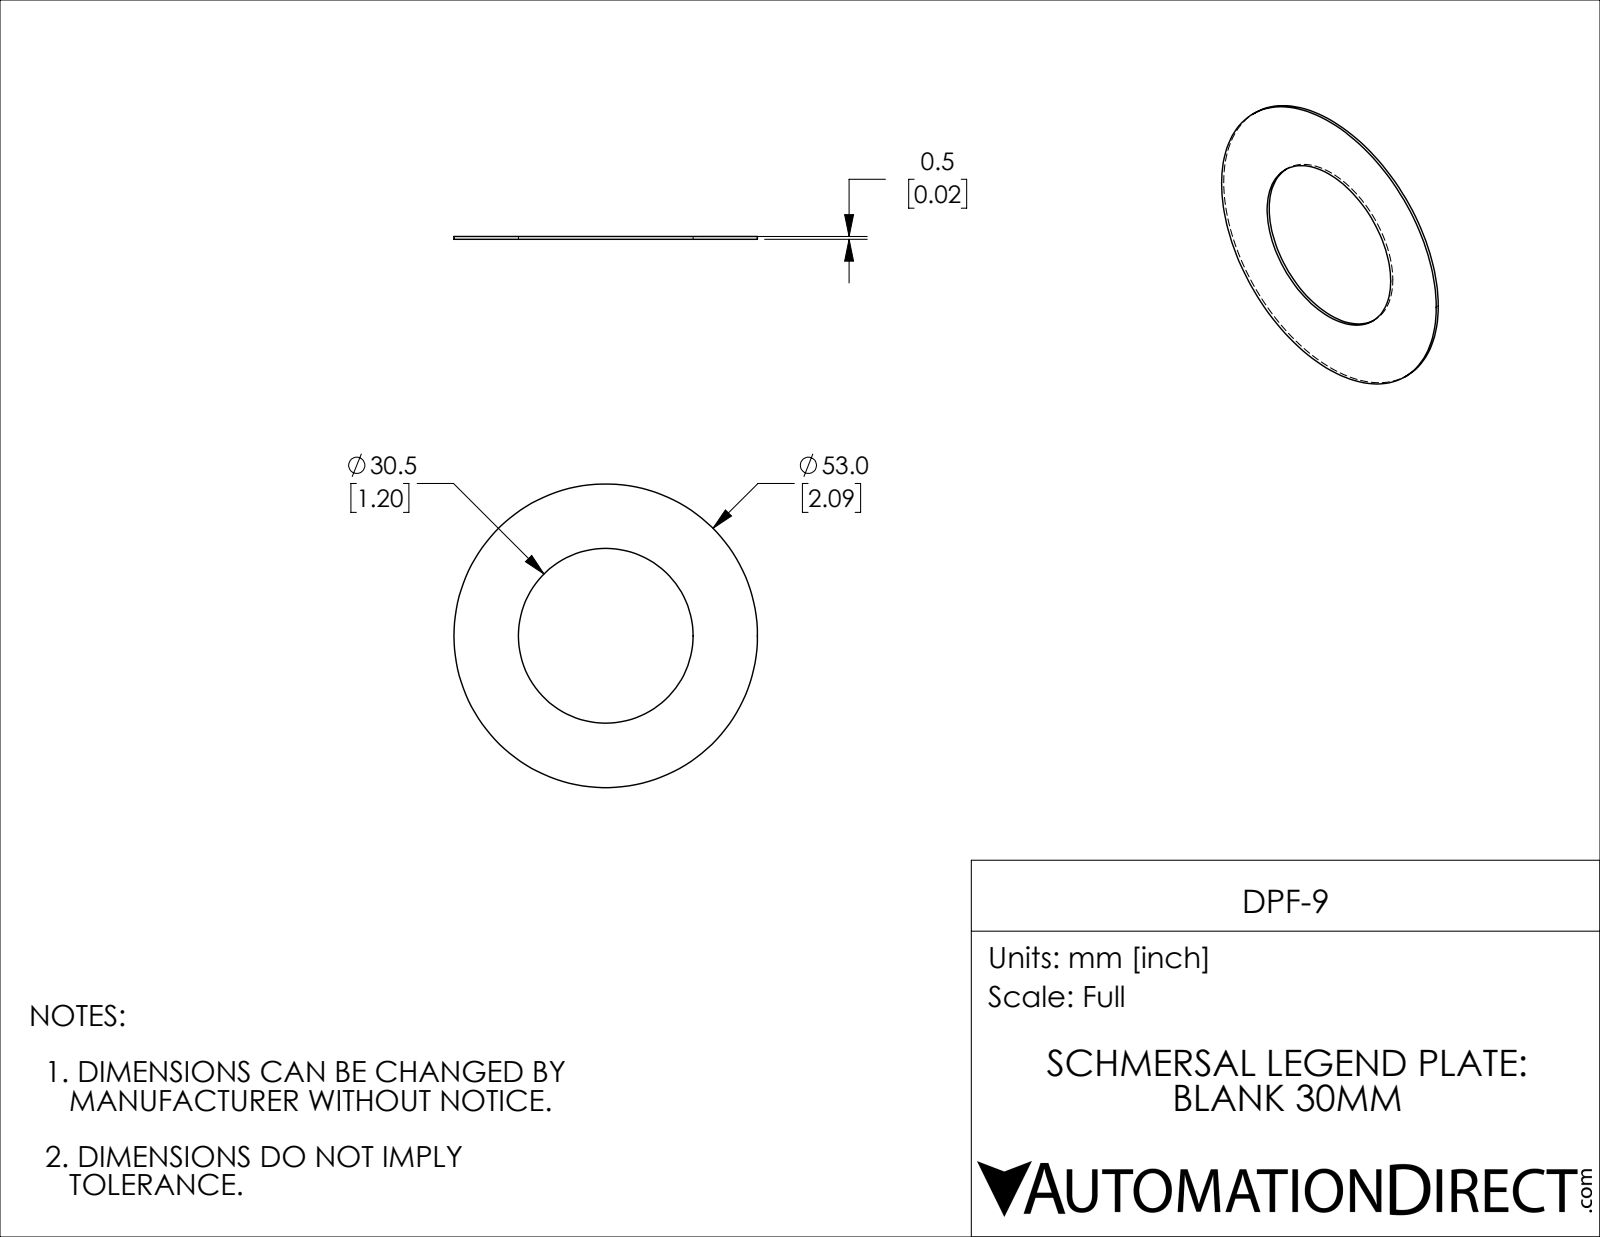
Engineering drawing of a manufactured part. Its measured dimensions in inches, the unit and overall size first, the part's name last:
Units: inches
Overall size (bounding box): 2.087 × 2.087 × 0.02
Round holes (diameter × count): ⌀1.201 ×1
Round bosses / shafts (diameter × count): ⌀2.087 ×1
Main face-to-face distances: 0.02
Volume: 0.045 in³ · Surface area: 4.778 in²
Bodies: 1 solid, 6 faces (2 planar, 4 cylindrical, 0 other)
Part name (STEP PRODUCT): DPF-9
STEP written by: SolidWorks 2019 (CONFIG_CONTROL_DESIGN)
